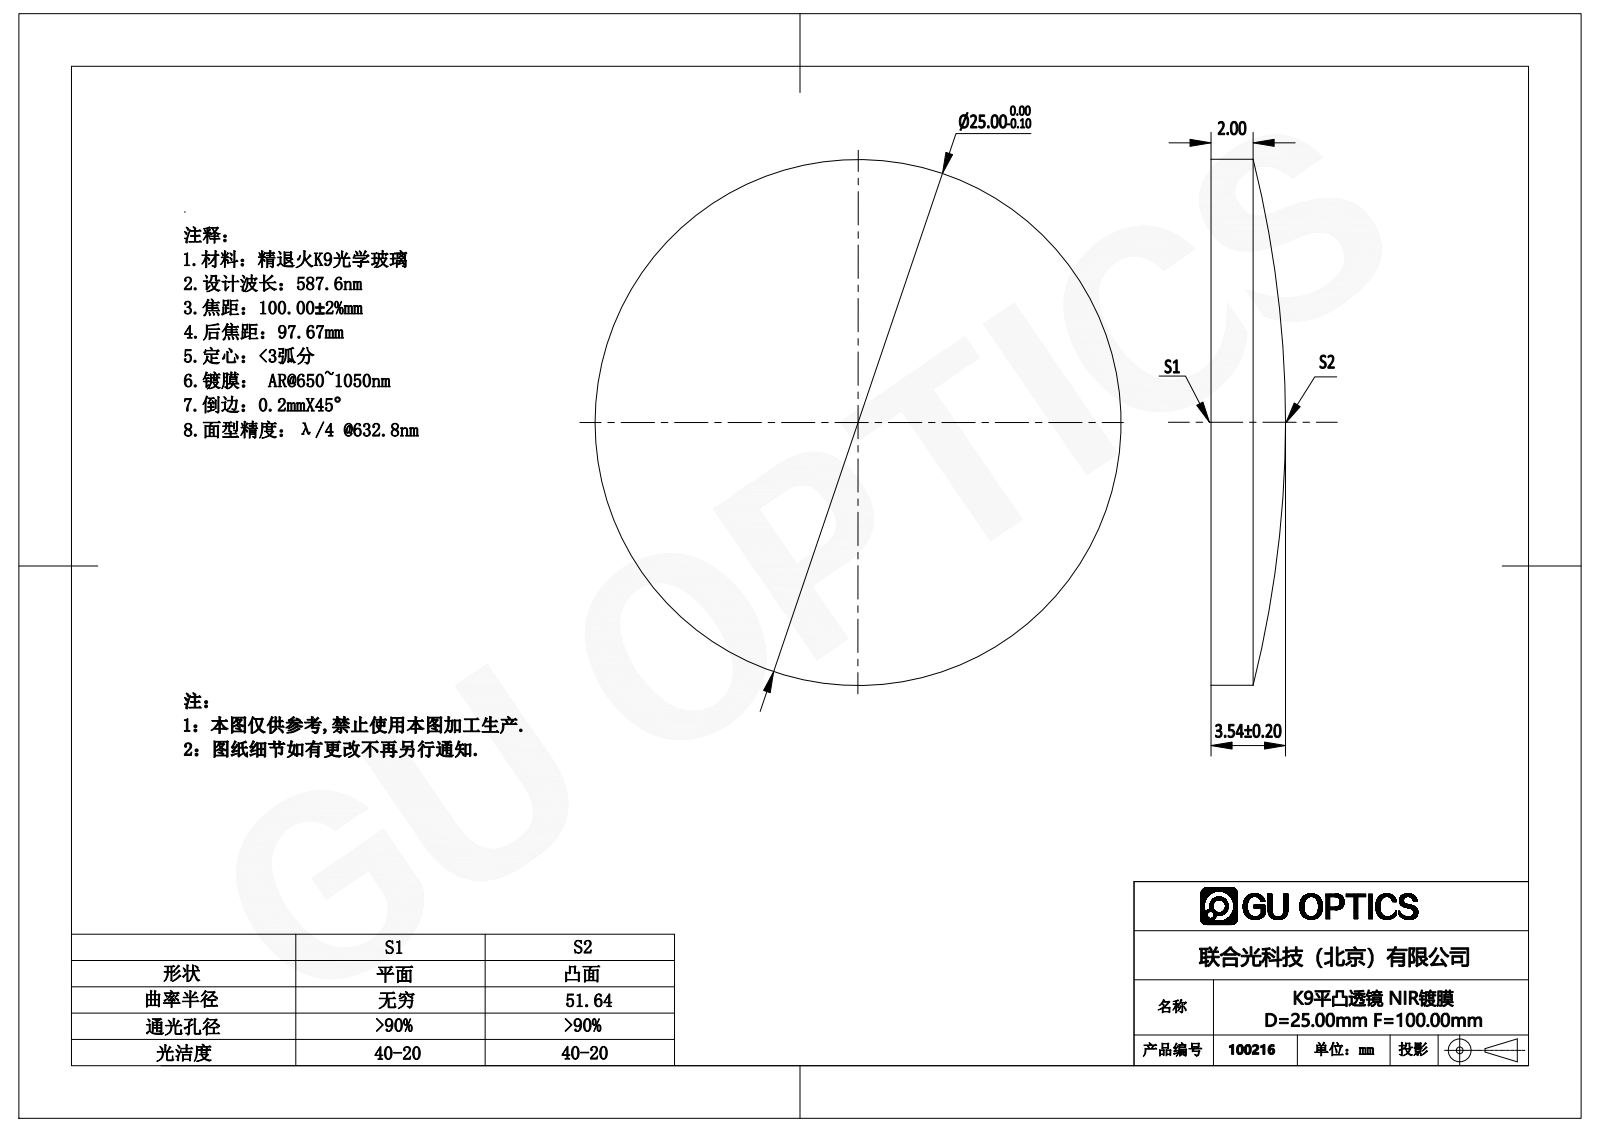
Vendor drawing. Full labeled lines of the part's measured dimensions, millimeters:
Part name (STEP PRODUCT): 100216
STEP written by: SolidWorks 2016 (AUTOMOTIVE_DESIGN)
Units: millimetres
Bodies: 1 solid, 5 faces (1 planar, 2 cylindrical, 2 other)
Overall size (bounding box): 25 × 25 × 3.54
Volume: 1 362 mm³ · Surface area: 1 146 mm²
Round bosses / shafts (diameter × count): ⌀25 ×1
